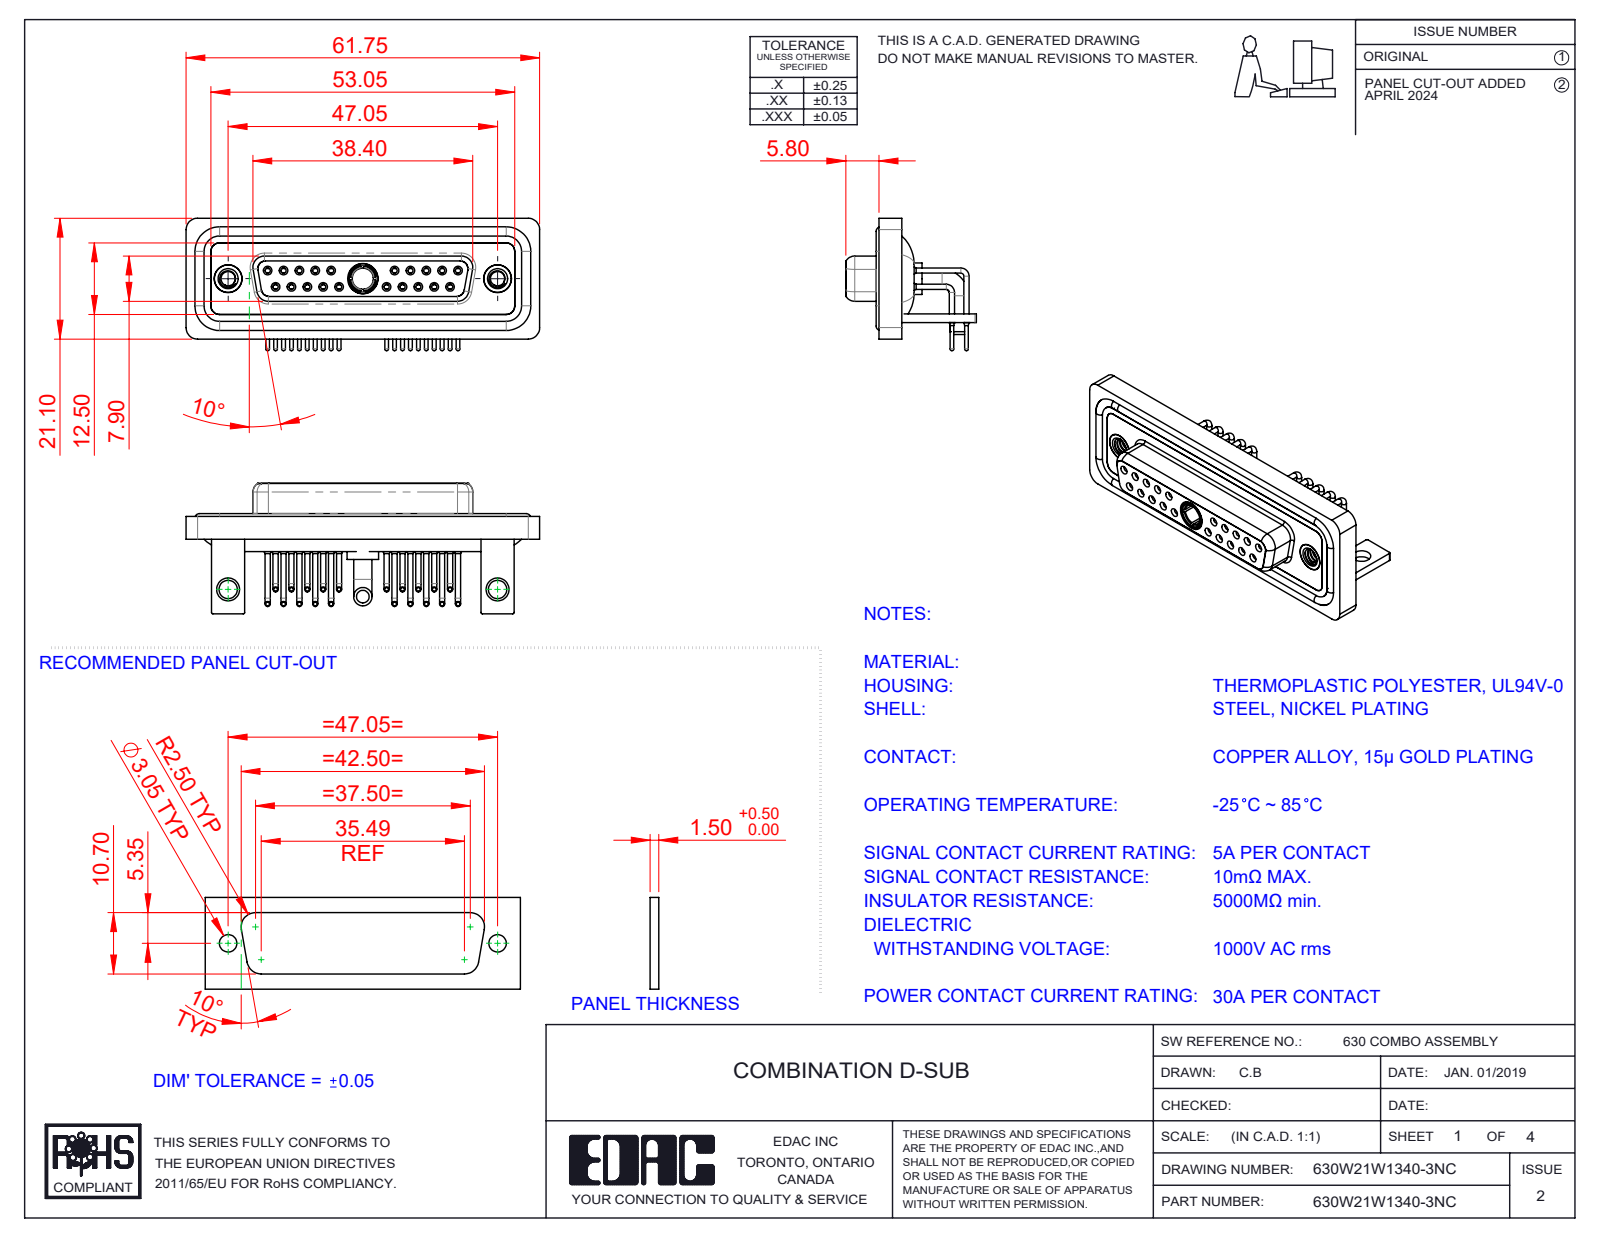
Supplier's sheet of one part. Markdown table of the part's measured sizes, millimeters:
| quantity | value |
| --- | --- |
| part name | 630Combo Threaded Rivet_A; 630Combo Housing_21W1; 630Combo Shell Front_25 Contacts; 630Combo Contact Row 2_50 Contacts (+6 more) |
| STEP written by | SolidWorks 2023 (CONFIG_CONTROL_DESIGN) |
| units | millimeters |
| bodies | 31 solids, 1566 faces (454 planar, 695 cylindrical, 417 other) |
| overall size | 61.75 × 23.12 × 22.8 |
| volume | 8 893 mm³ |
| surface area | 15 537 mm² |
| round holes (diameter × count) | 0.9 × 20, 1.1 × 20, 1.5 × 20, 2 × 20, 1.6 × 10, 1.7 × 10, 4.85 × 3, 2.5 × 2, 3.2 × 2, 4 × 2, 4.05 × 2, 5 × 2 |
| round bosses / shafts (diameter × count) | 0.9 × 20, 0.65 × 20, 1.6 × 14, 4.95 × 2, 4.8 × 2, 3.2 × 2, 5.5 × 1, 5.2 × 1 |
| partial cylindrical surfaces (radius × count) | 2 × 19, 1.5 × 18, 0.25 × 16, 1.35 × 8, 1.6 × 8, 0.5 × 5, 0.6 × 4, 0.65 × 4 |
| main face-to-face distances | 0.4, 1.8, 2.9, 3.7, 1.5, 4.1, 1.1, 1.4, 1.6, 2.5 |
| hole center spacings | 3.16, 2.77, 5.54, 8.31, 5.04, 19.39, 20.97, 22.16 |
